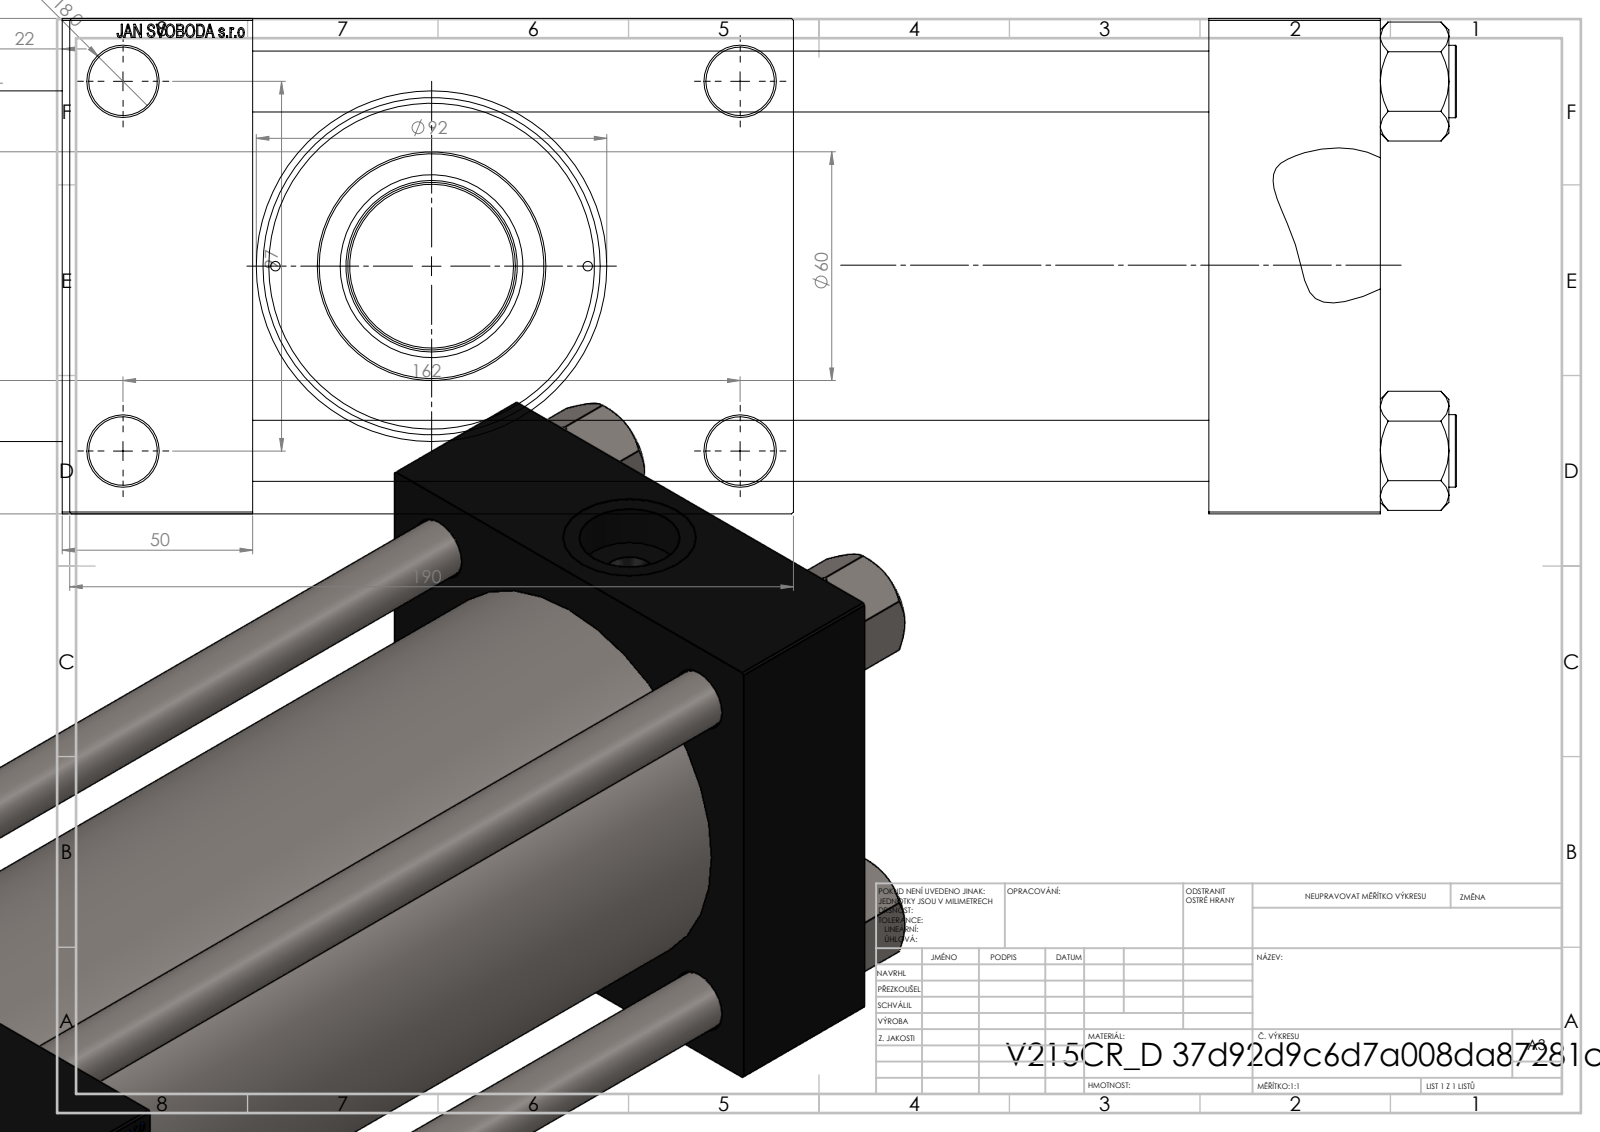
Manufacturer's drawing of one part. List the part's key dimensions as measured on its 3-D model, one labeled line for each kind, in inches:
Part name (STEP PRODUCT): V215CR_ROD_END_F; V215CR_VCP_D; NUT_M5_D; V215CR_D_Body (+2 more)
STEP written by: SolidWorks 2019 (CONFIG_CONTROL_DESIGN)
Units: inches
Bodies: 12 solids, 1173 faces (550 planar, 97 cylindrical, 526 other)
Overall size (bounding box): 18.386 × 7.48 × 5.118
Volume: 199.2 in³ · Surface area: 835.1 in²
Round holes (diameter × count): ⌀0.63 ×4, ⌀0.709 ×4, ⌀0.098 ×2, ⌀0.276 ×2, ⌀1.041 ×2, ⌀1.378 ×2, ⌀1.24 ×1, ⌀1.772 ×1, ⌀1.89 ×1, ⌀2.992 ×1, ⌀3.366 ×1, ⌀3.937 ×1
Round bosses / shafts (diameter × count): ⌀0.748 ×4, ⌀4.173 ×1, ⌀3.622 ×1, ⌀2.362 ×1, ⌀1.732 ×1, ⌀1.299 ×1
Main face-to-face distances: 5.118, 1.772, 11.654, 9.882, 13.622, 11.85, 1.969, 1.181, 6.299, 7.48
Hole centre spacings: 1.281, 1.93, 2.475, 2.698, 3.717, 3.815, 4.005, 4.026
